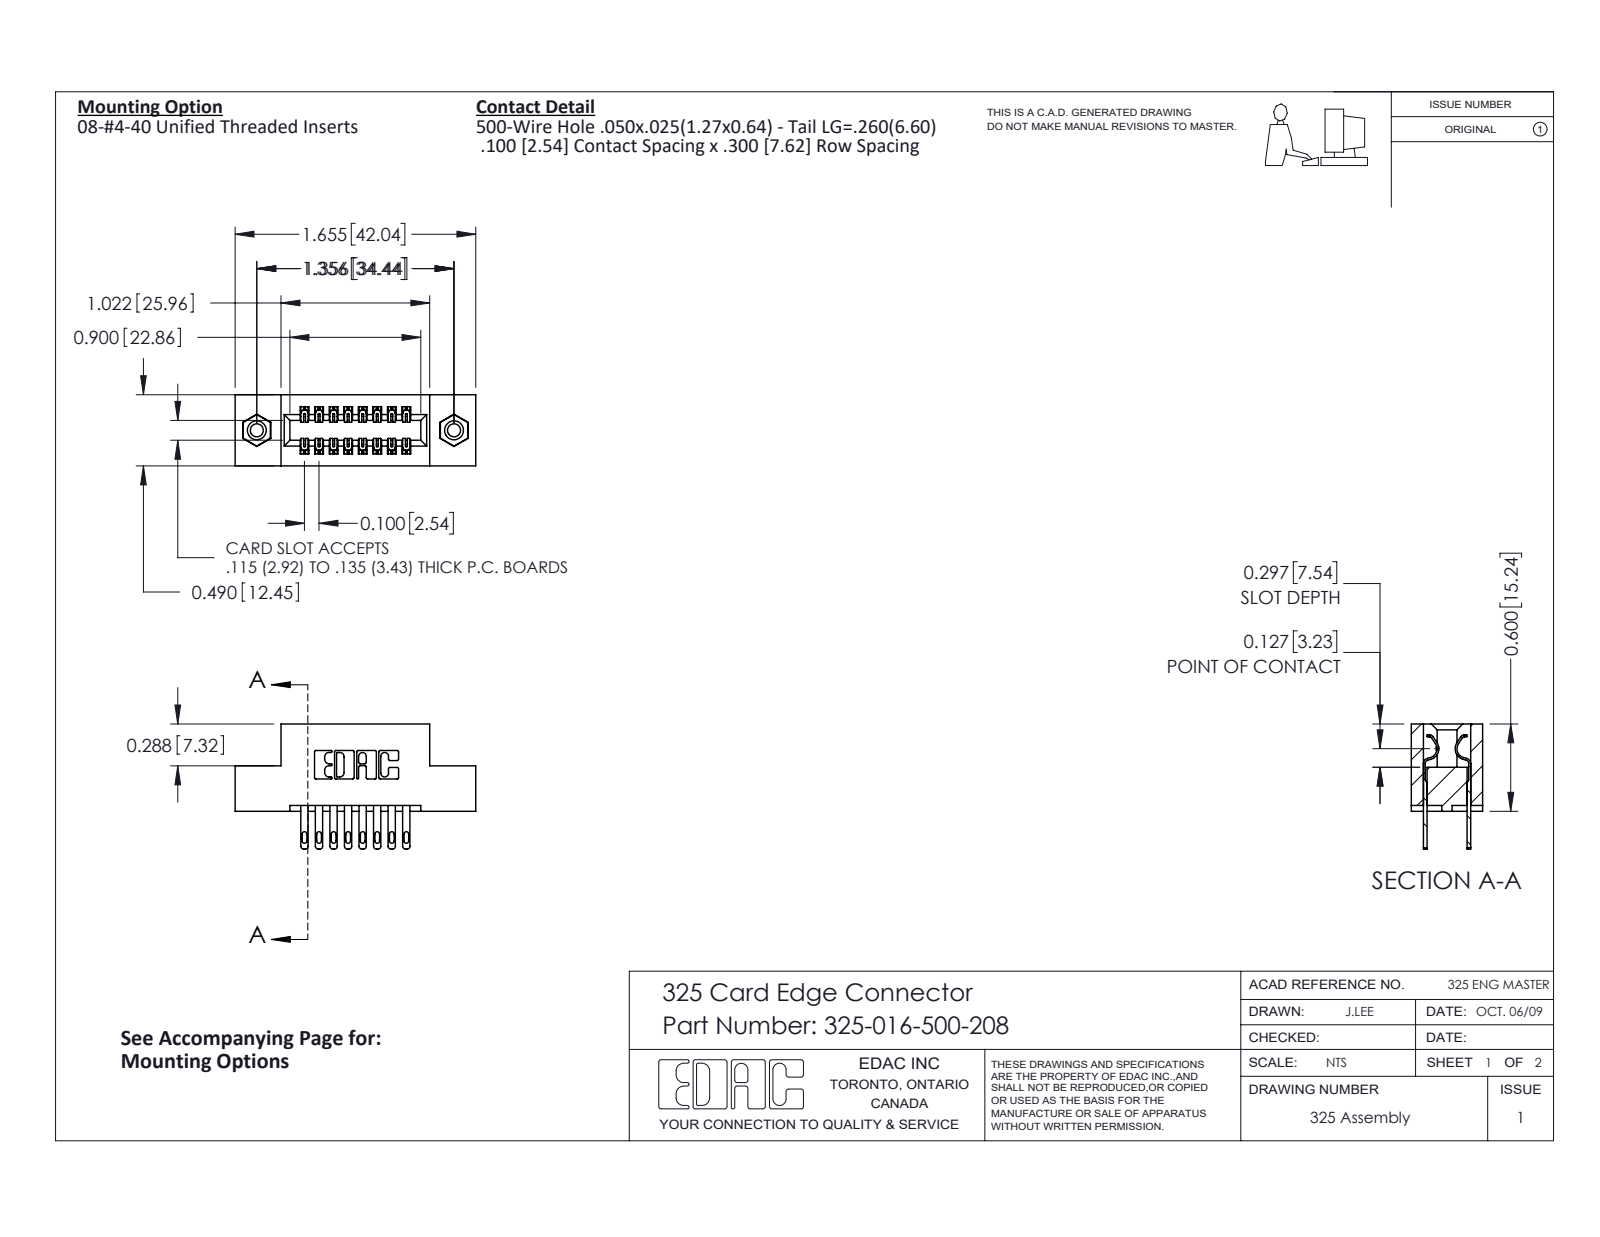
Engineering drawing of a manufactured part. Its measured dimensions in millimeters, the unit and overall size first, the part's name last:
Units: millimetres
Overall size (bounding box): 42 × 21.8 × 12.4
Round holes (diameter × count): ⌀2.3 ×2, ⌀3.2 ×2, ⌀4.1 ×2
Round bosses / shafts (diameter × count): ⌀3.9 ×2
Partial cylindrical surfaces — rounded edges, fillets, slot ends (radius × count): R0.2 ×24, R0.3 ×22, R0.4 ×16, R0.5 ×16, R0.2 ×6, R0.8 ×6, R0.7 ×3, R0.4 ×2
Main face-to-face distances: 7.6, 2.1, 10.3, 2.5, 5.1, 1, 12.4, 2.7, 9.7, 0.6
Hole centre spacings: 34.4
Volume: 5 160 mm³ · Surface area: 5 625 mm²
Bodies: 19 solids, 942 faces (582 planar, 344 cylindrical, 16 other)
Part name (STEP PRODUCT): 325-016-500-208; 325-292-001_325-293-100; 325 Part_TI; 345-250-001_345-250-003-102
STEP written by: SolidWorks 2016 (CONFIG_CONTROL_DESIGN)
